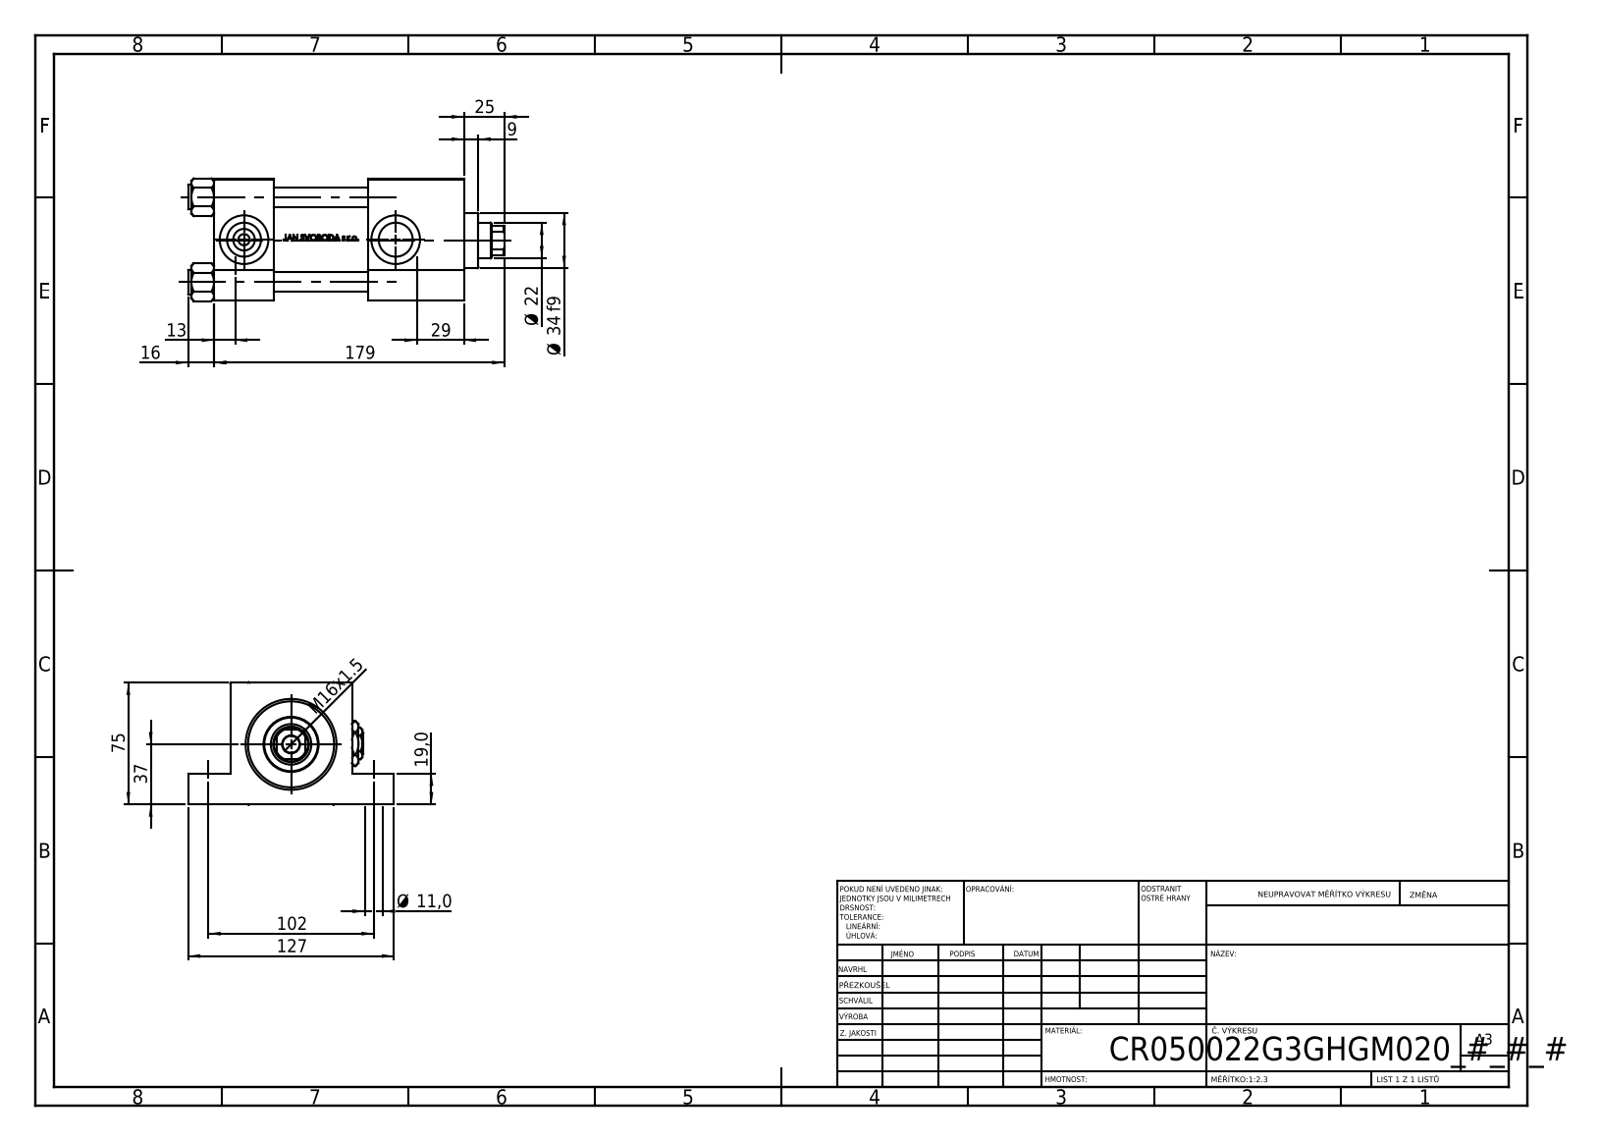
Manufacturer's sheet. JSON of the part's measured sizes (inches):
{"part_name": "NUT_M5_G; V215CR_G_TYCINKA; Zatka_pro_OIL_PORT; V215_VC_A (+2 more)", "step_written_by": "SolidWorks 2019 (CONFIG_CONTROL_DESIGN)", "units": "inches", "bodies": {"solids": 13, "faces": 1183, "planar": 477, "cylindrical": 132, "other": 574}, "overall_size": [7.677, 5, 2.974], "volume_in3": 45.78, "surface_area_in2": 254.1, "round_holes": [[0.472, 4], [0.433, 3], [0.276, 2], [0.825, 2], [1.181, 2], [0.413, 1], [0.433, 1], [0.866, 1], [0.984, 1], [1.614, 1], [1.969, 1], [2.087, 1]], "round_bosses_or_shafts": [[0.591, 4], [2.205, 1], [1.339, 1]], "partial_cylinders_radius": [[0.413, 1]], "face_to_face_distances": [2.953, 1.457, 6.063, 4.606, 0.748, 2.205, 3.74, 2.283, 2.323, 1.024], "hole_center_spacings": [2.059, 1.442, 1.47, 2.912, 4.016, 4.409, 5.964, 3.681]}
